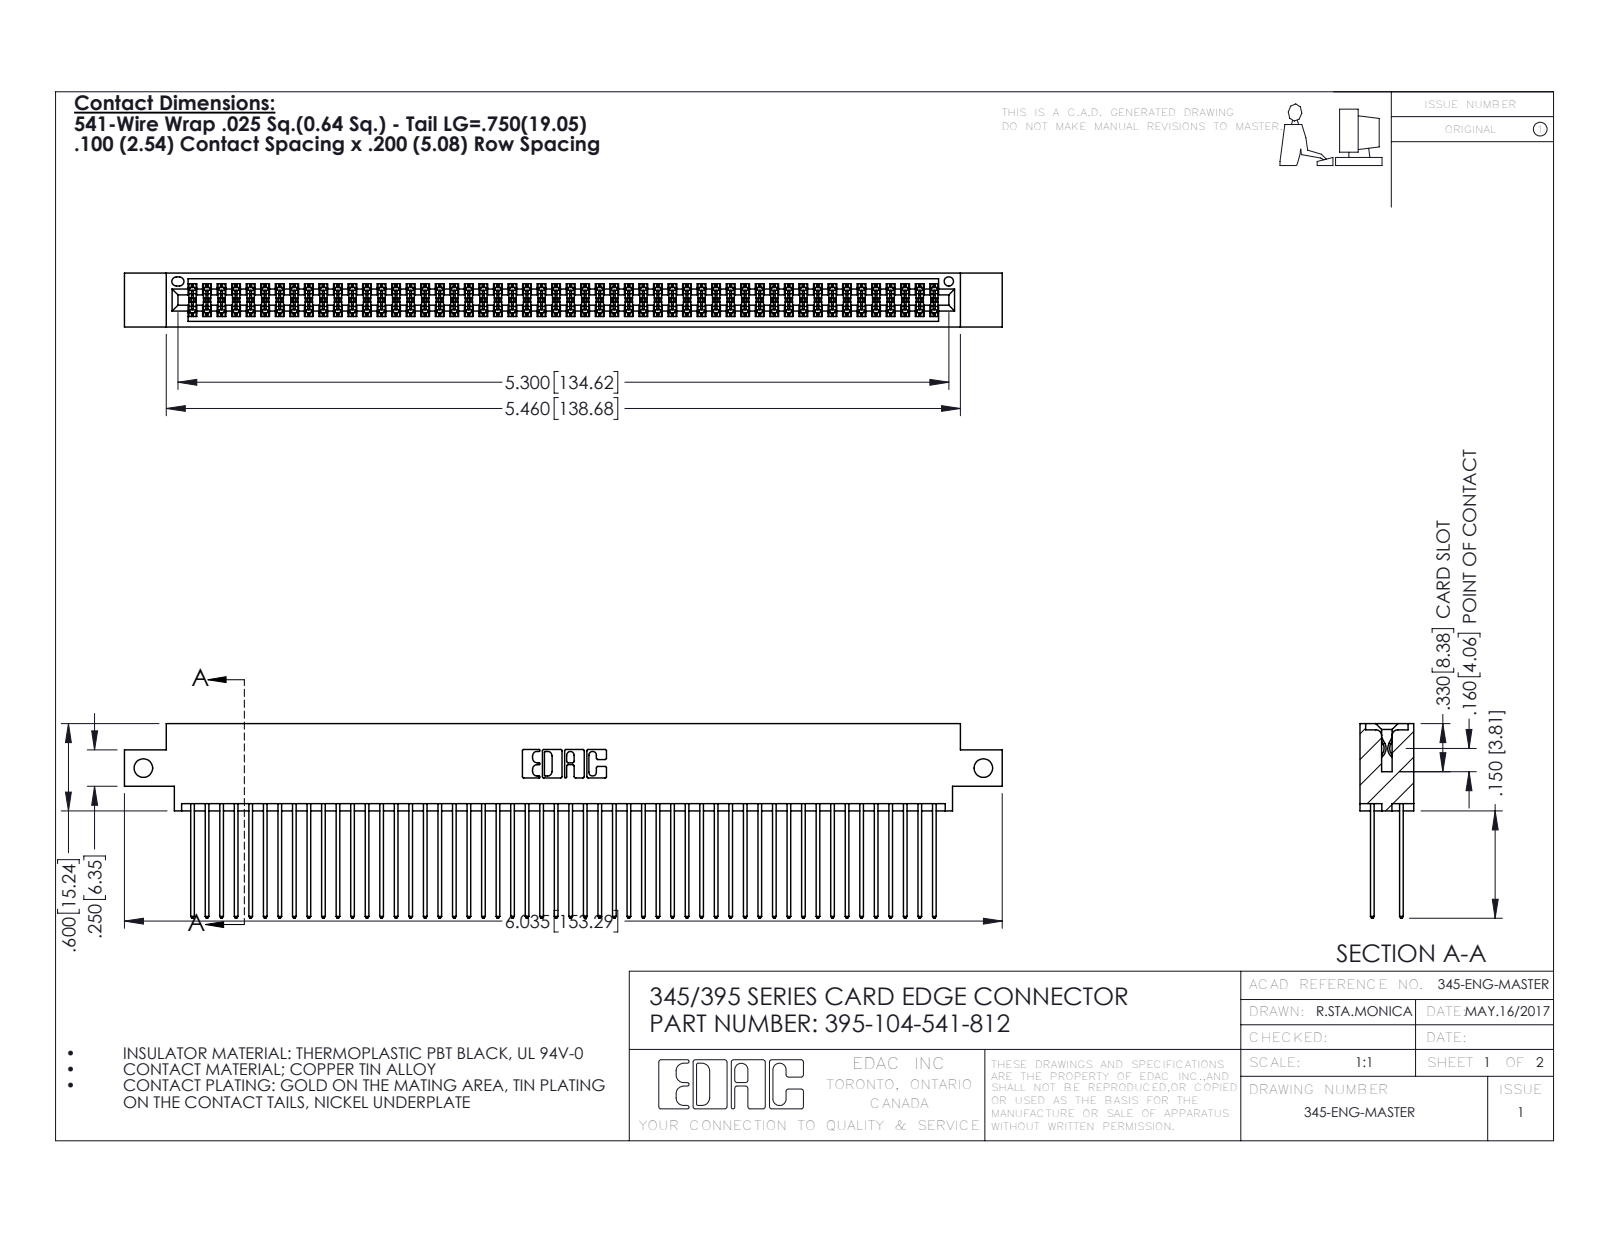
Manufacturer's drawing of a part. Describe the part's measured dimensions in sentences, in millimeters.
The part is named "345-292-001_345-293-141; 345 Part_0.170 Offset - Side Mount; 395-104-541-812". Its 3-D file was written by "SolidWorks 2016 (CONFIG_CONTROL_DESIGN)". It is 105 solids with 5330 faces: 3516 planar, 1814 cylindrical and 0 other. Overall it measures 153.3 by 34 by 9.4 millimeters. Its volume is 15 400 cubic millimeters and its surface area 25 740 square millimeters. Round holes: 2 of diameter 3.3, 1 of diameter 1.6. Partial cylindrical surfaces (rounded edges, fillets, slot ends): 156 of radius 0.2, 104 of radius 0.3, 22 of radius 0.3, 6 of radius 0.2, 6 of radius 0.8, 3 of radius 0.7, 2 of radius 0.4, 2 of radius 0.5. The main face-to-face distances are 1.8, 7.6, 5.1, 2.5, 6.9, 0.6, 5.7, 9.4, 4.4, 3.8. The hole center spacings are 146.7.
